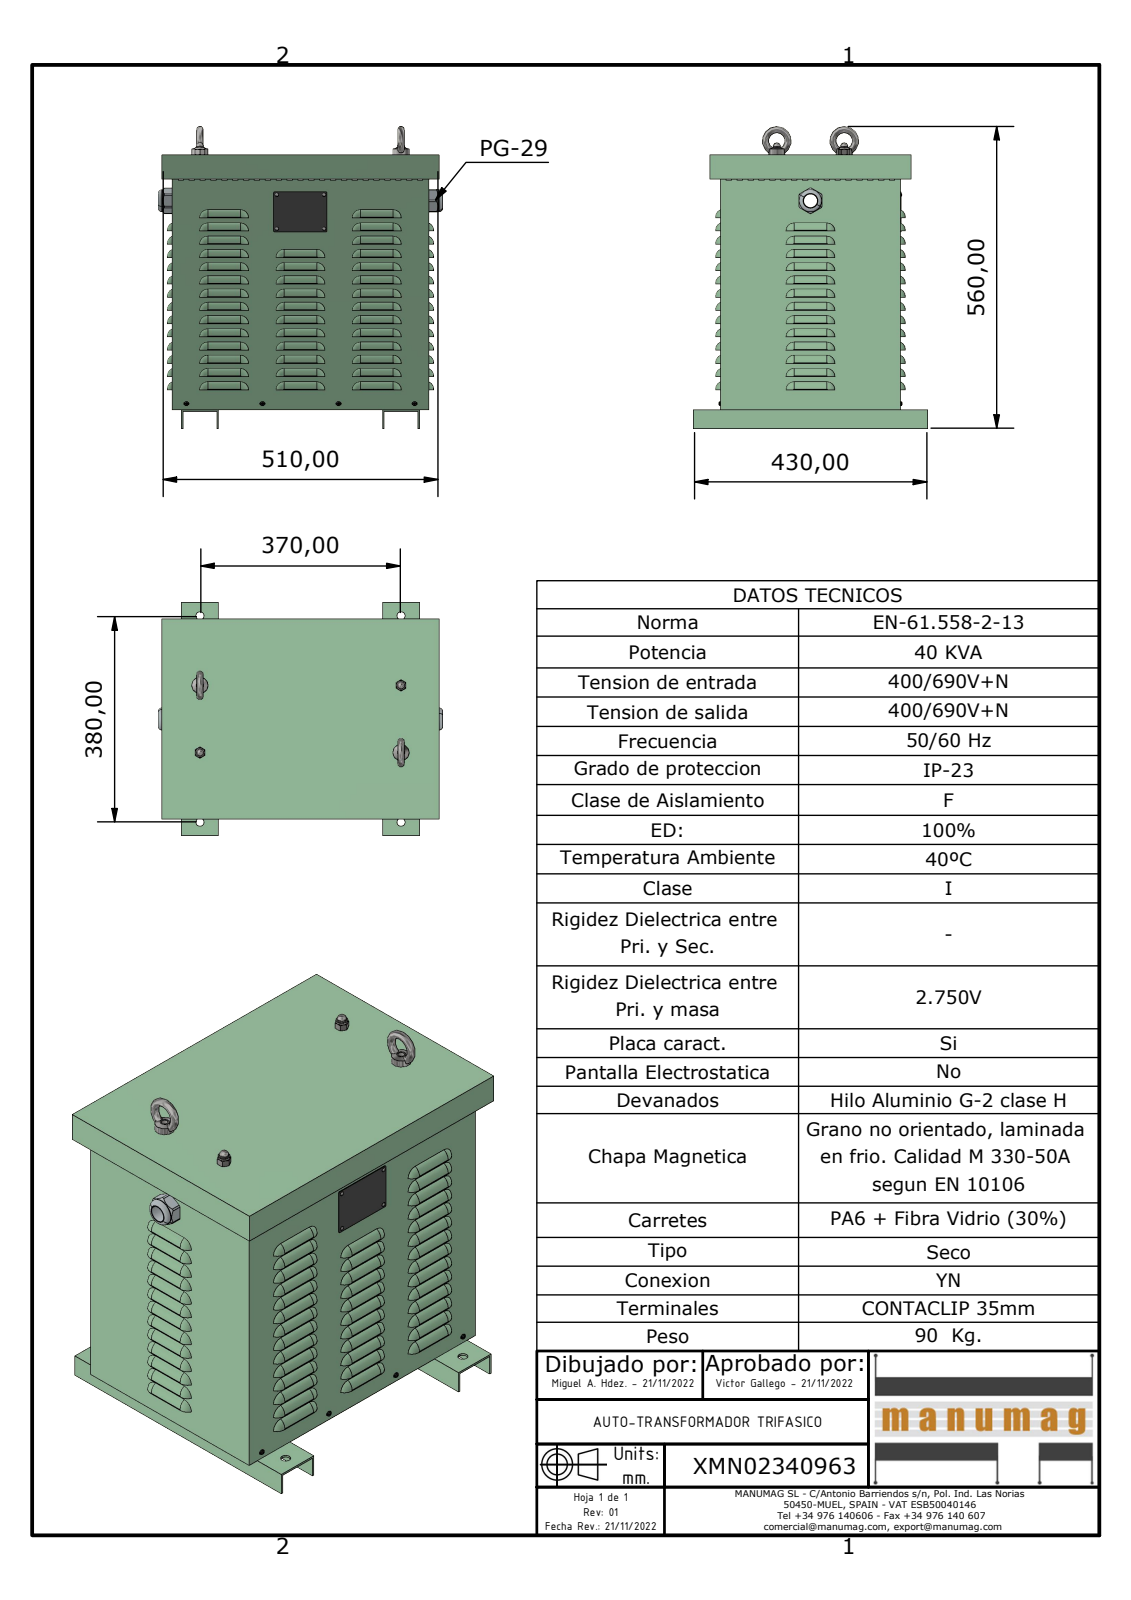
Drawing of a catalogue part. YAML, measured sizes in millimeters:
part_name: "XMN02340963; JE040 - JE050 CUERPO; JE040 - JE050 BASE; JE040 - JE050 PATAS (+7 more)"
step_written_by: "Autodesk Inventor 2023 (AUTOMOTIVE_DESIGN)"
units: millimeters
bodies: {solids: 24, faces: 2403, planar: 969, cylindrical: 808, other: 626}
overall_size: [560, 523.4, 431]
volume: 3115000
surface_area: 2768000
round_holes:
  - {diameter: 11, count: 260}
  - {diameter: 4, count: 4}
  - {diameter: 5, count: 4}
  - {diameter: 10.11, count: 4}
  - {diameter: 14, count: 4}
  - {diameter: 15, count: 4}
  - {diameter: 25, count: 1}
  - {diameter: 38, count: 1}
round_bosses_or_shafts:
  - {diameter: 4, count: 4}
  - {diameter: 3.62, count: 4}
  - {diameter: 3.2, count: 4}
  - {diameter: 30, count: 2}
  - {diameter: 18, count: 2}
  - {diameter: 13.6, count: 2}
  - {diameter: 40.8, count: 1}
  - {diameter: 37.3, count: 1}
partial_cylinders:
  - {radius: 14, count: 104}
  - {radius: 7, count: 54}
  - {radius: 15, count: 54}
  - {radius: 3.22, count: 12}
  - {radius: 2.5, count: 8}
  - {radius: 7.5, count: 8}
  - {radius: 2, count: 4}
  - {radius: 23.85, count: 1}
face_to_face_distances: [2, 470, 472, 329, 468, 327, 331, 3, 19.5, 348.5]
hole_center_spacings: [31.76, 71.59, 15, 28, 70, 44.6, 99.14, 140.8]
